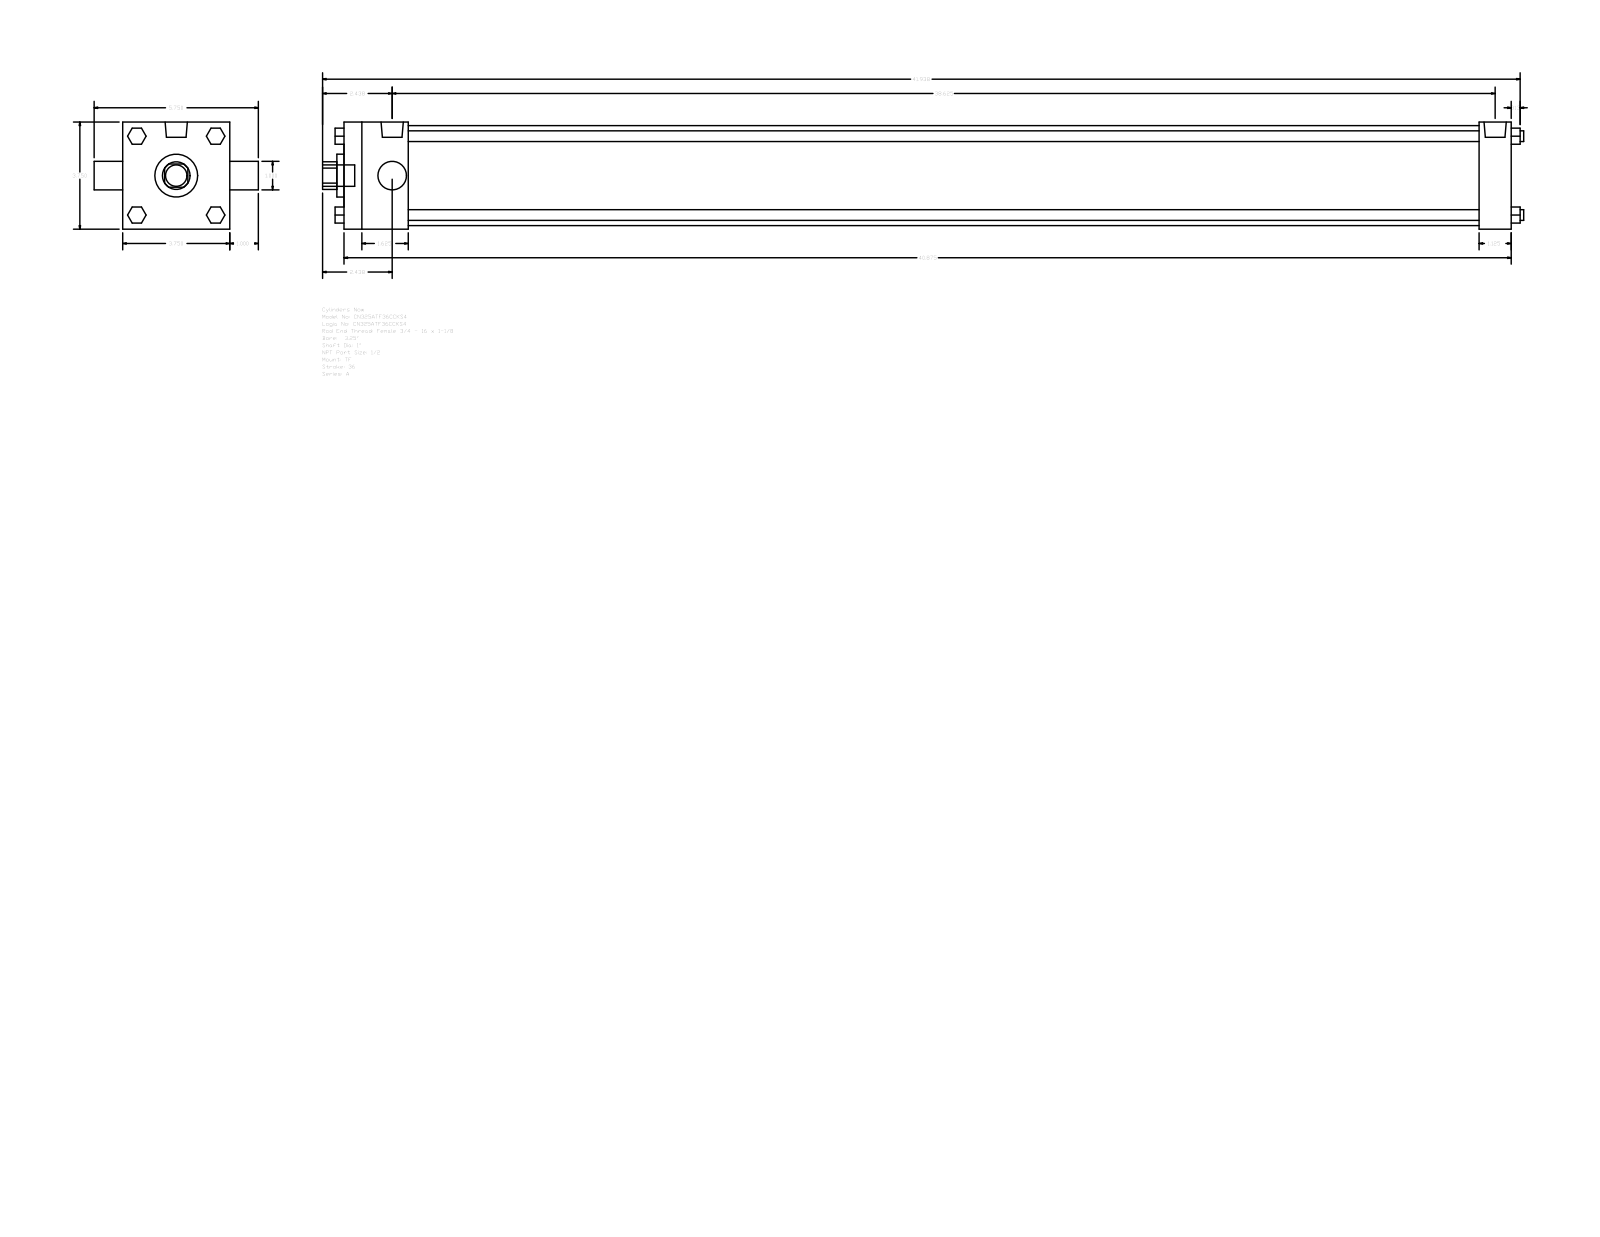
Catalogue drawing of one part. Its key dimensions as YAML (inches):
part_name: "A_TF__0325_1"
step_written_by: "GSSL Pune (CONFIG_CONTROL_DESIGN)"
units: inches
bodies: {solids: 0, faces: 120, planar: 92, cylindrical: 28, other: 0}
overall_size: [42.063, 5.75, 3.75]
round_holes:
  - {diameter: 1, count: 2}
  - {diameter: 1.5, count: 1}
  - {diameter: 3.5, count: 1}
round_bosses_or_shafts:
  - {diameter: 0.375, count: 4}
  - {diameter: 0.344, count: 3}
  - {diameter: 0.778, count: 2}
  - {diameter: 0.75, count: 1}
partial_cylinders:
  - {radius: 0.484, count: 1}
face_to_face_distances: [3.75, 40.875, 2.25, 39.75, 37.5, 38.625, 1.125, 0.562, 1.38, 2.39]
